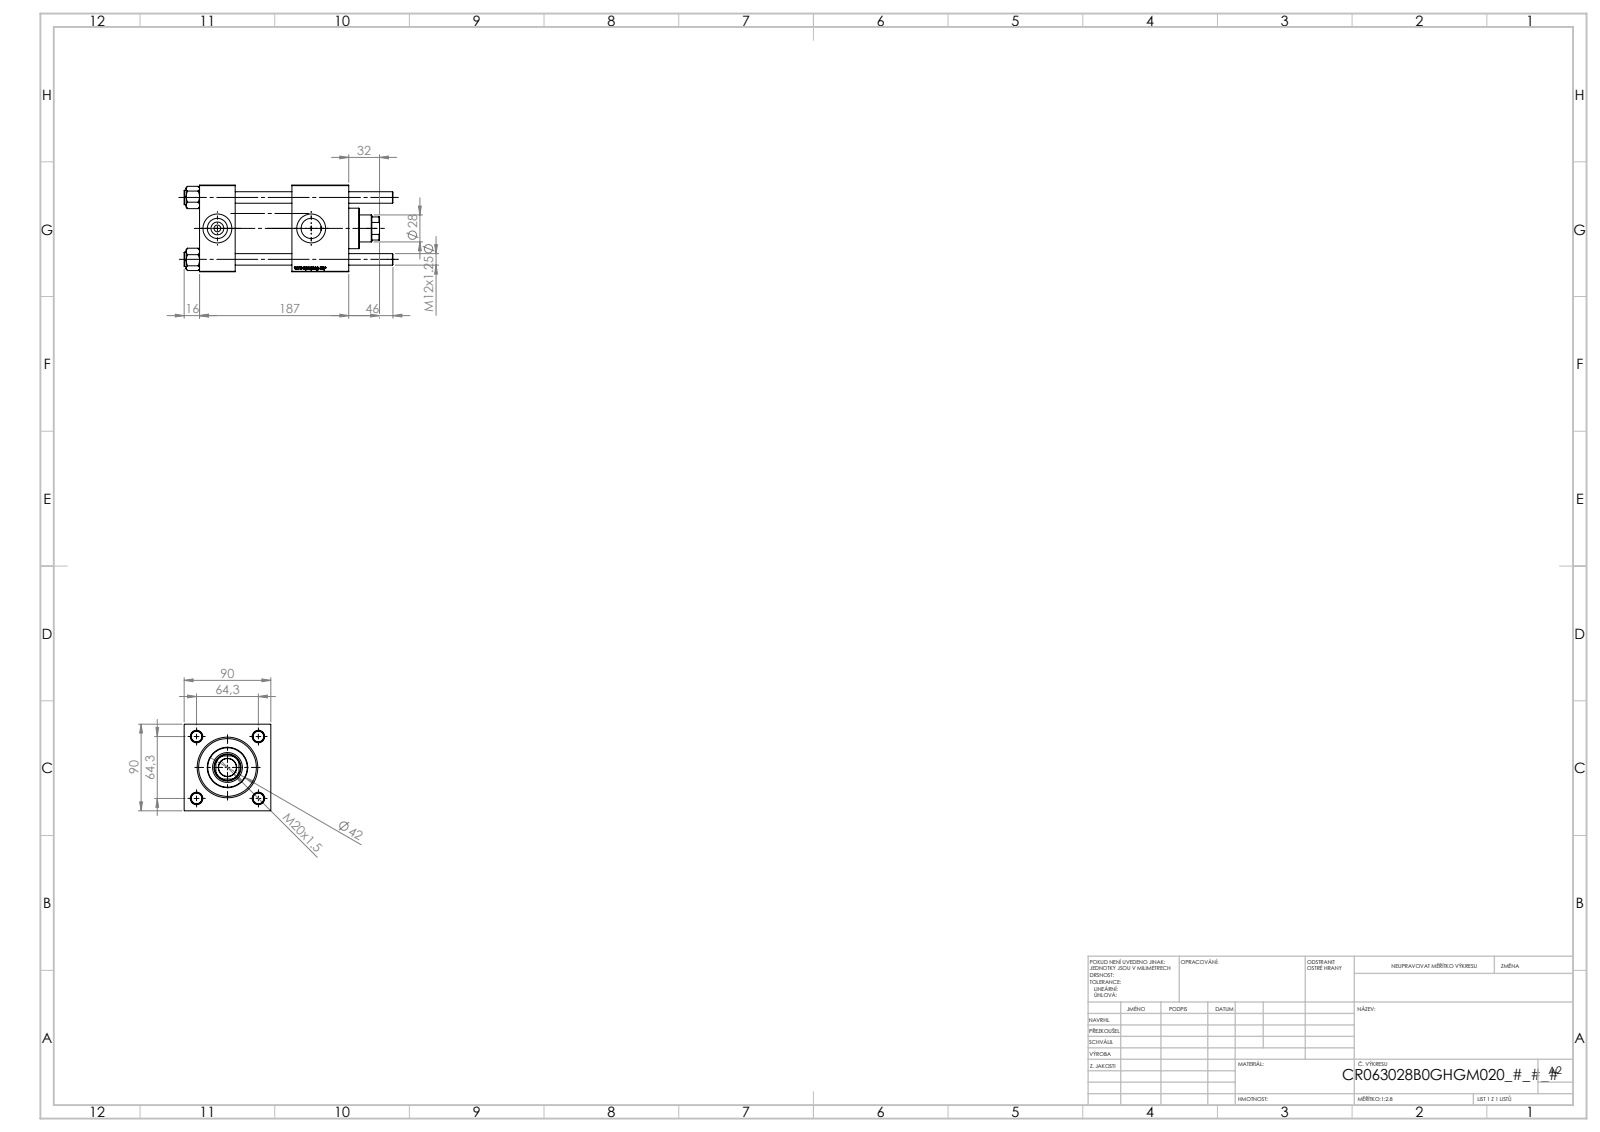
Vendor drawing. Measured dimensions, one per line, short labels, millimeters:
name: V215CR_VCP_B; V215_VC_A; V215CR_B_TYCINKA; V215CR_B-1 (+1 more)
written by: SolidWorks 2019 (CONFIG_CONTROL_DESIGN)
unit: mm
bodies: 11 solids, 1158 faces (432 planar, 78 cylindrical, 648 other)
size: 217 × 90 × 90
volume: 981 346 mm³; area: 195 012 mm²
holes: 4× ⌀12, 2× ⌀7, 2× ⌀20.96, 2× ⌀30, 1× ⌀18.5, 1× ⌀28, 1× ⌀31, 1× ⌀50, 1× ⌀60, 1× ⌀63
bosses: 4× ⌀15, 1× ⌀69, 1× ⌀42
rounds: 1× R13.5
face distances: 90, 59, 37, 155, 118, 96, 126.3, 89.3, 30.3, 28.7
hole spacings: 45.47, 64.3, 90.93, 97.5
